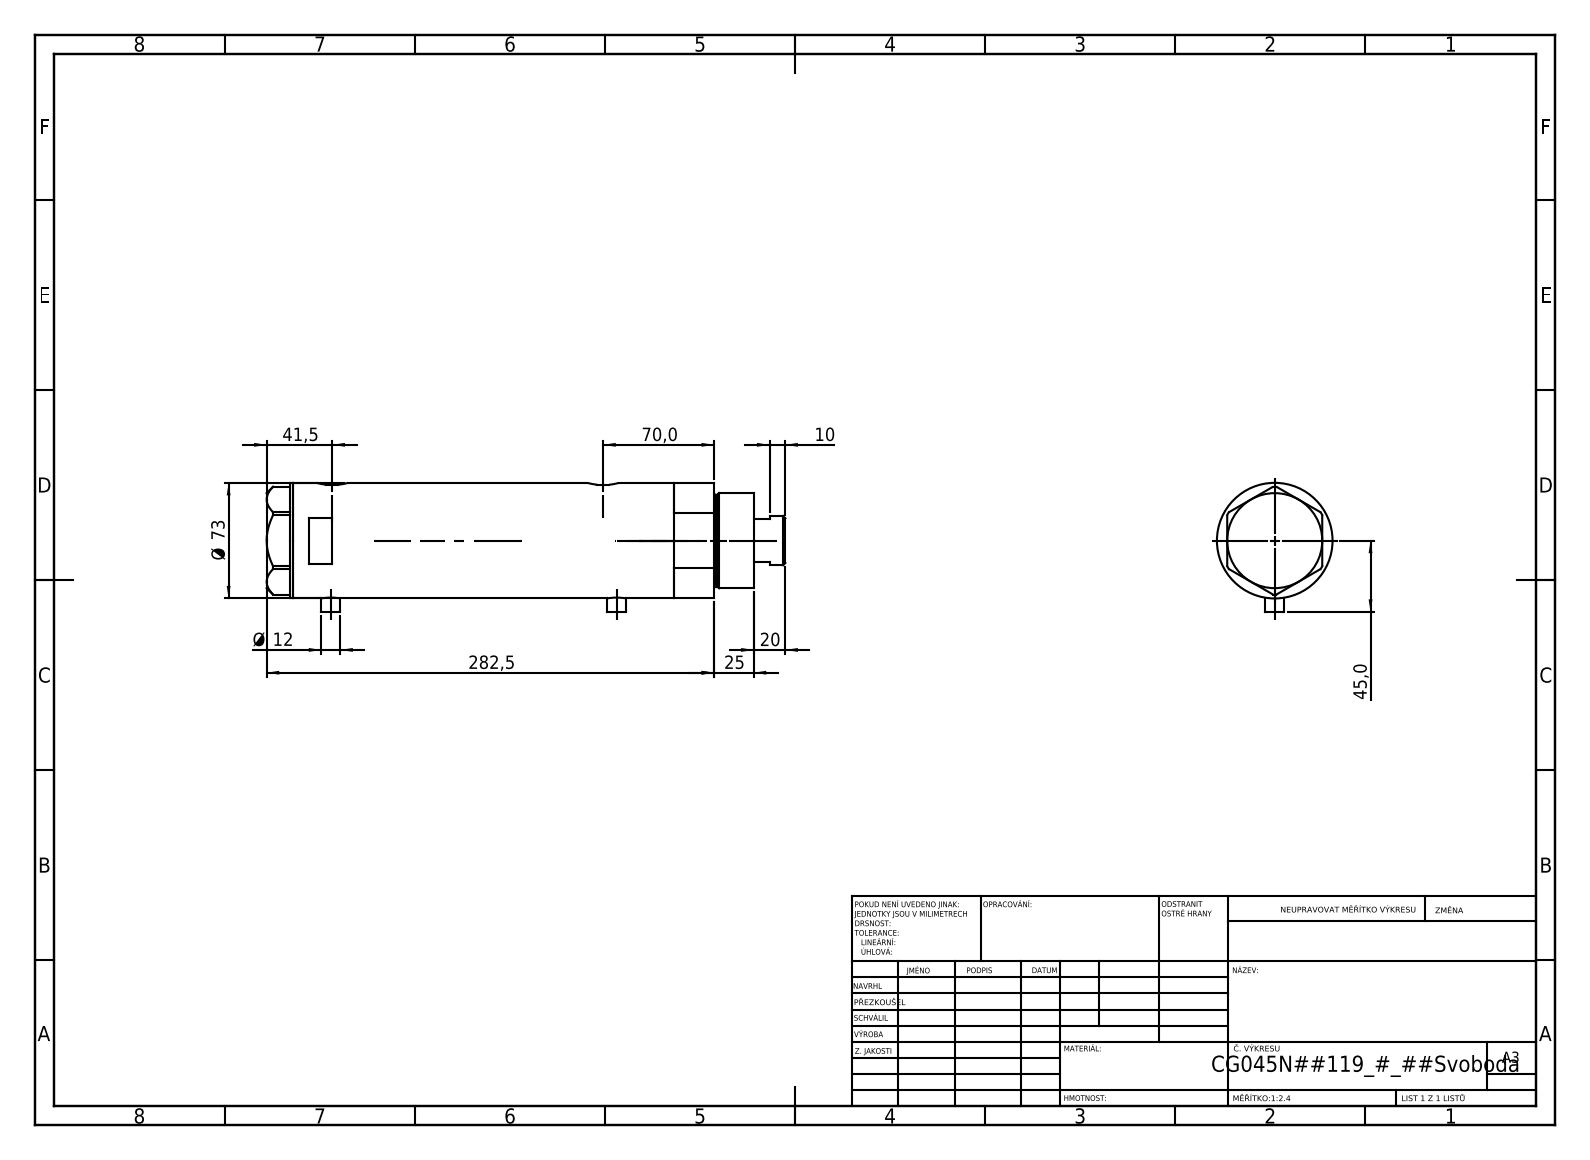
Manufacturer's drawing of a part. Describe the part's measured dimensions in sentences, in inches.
The part is named "V270CG_VC; V270CG_BACK; V270CG_FRONT; V270CG_MIDDLE". Its 3-D file was written by "SolidWorks 2019 (CONFIG_CONTROL_DESIGN)". It is 4 solids with 125 faces: 50 planar, 55 cylindrical and 20 other. Overall it measures 12.894 by 3.209 by 2.874 inches. Its volume is 69.87 cubic inches and its surface area 286.7 square inches. Round holes: 2 of diameter 0.197, 2 of diameter 0.492, 2 of diameter 0.518, 1 of diameter 0.413, 1 of diameter 1.26, 1 of diameter 1.319, 1 of diameter 1.772, 1 of diameter 1.89, 1 of diameter 2.52. Round bosses or shafts: 2 of diameter 0.472, 1 of diameter 2.874, 1 of diameter 2.362, 1 of diameter 2.283, 1 of diameter 1.22. Partial cylindrical surfaces (rounded edges, fillets, slot ends): 2 of radius 0.394. The main face-to-face distances are 7.717, 1.024, 6.693, 0.65, 1.673, 8.366, 0.079, 11.457, 12.106, 10.433. The hole center spacings are 0.039, 0.335, 6.732, 6.772, 7.067, 7.106.
